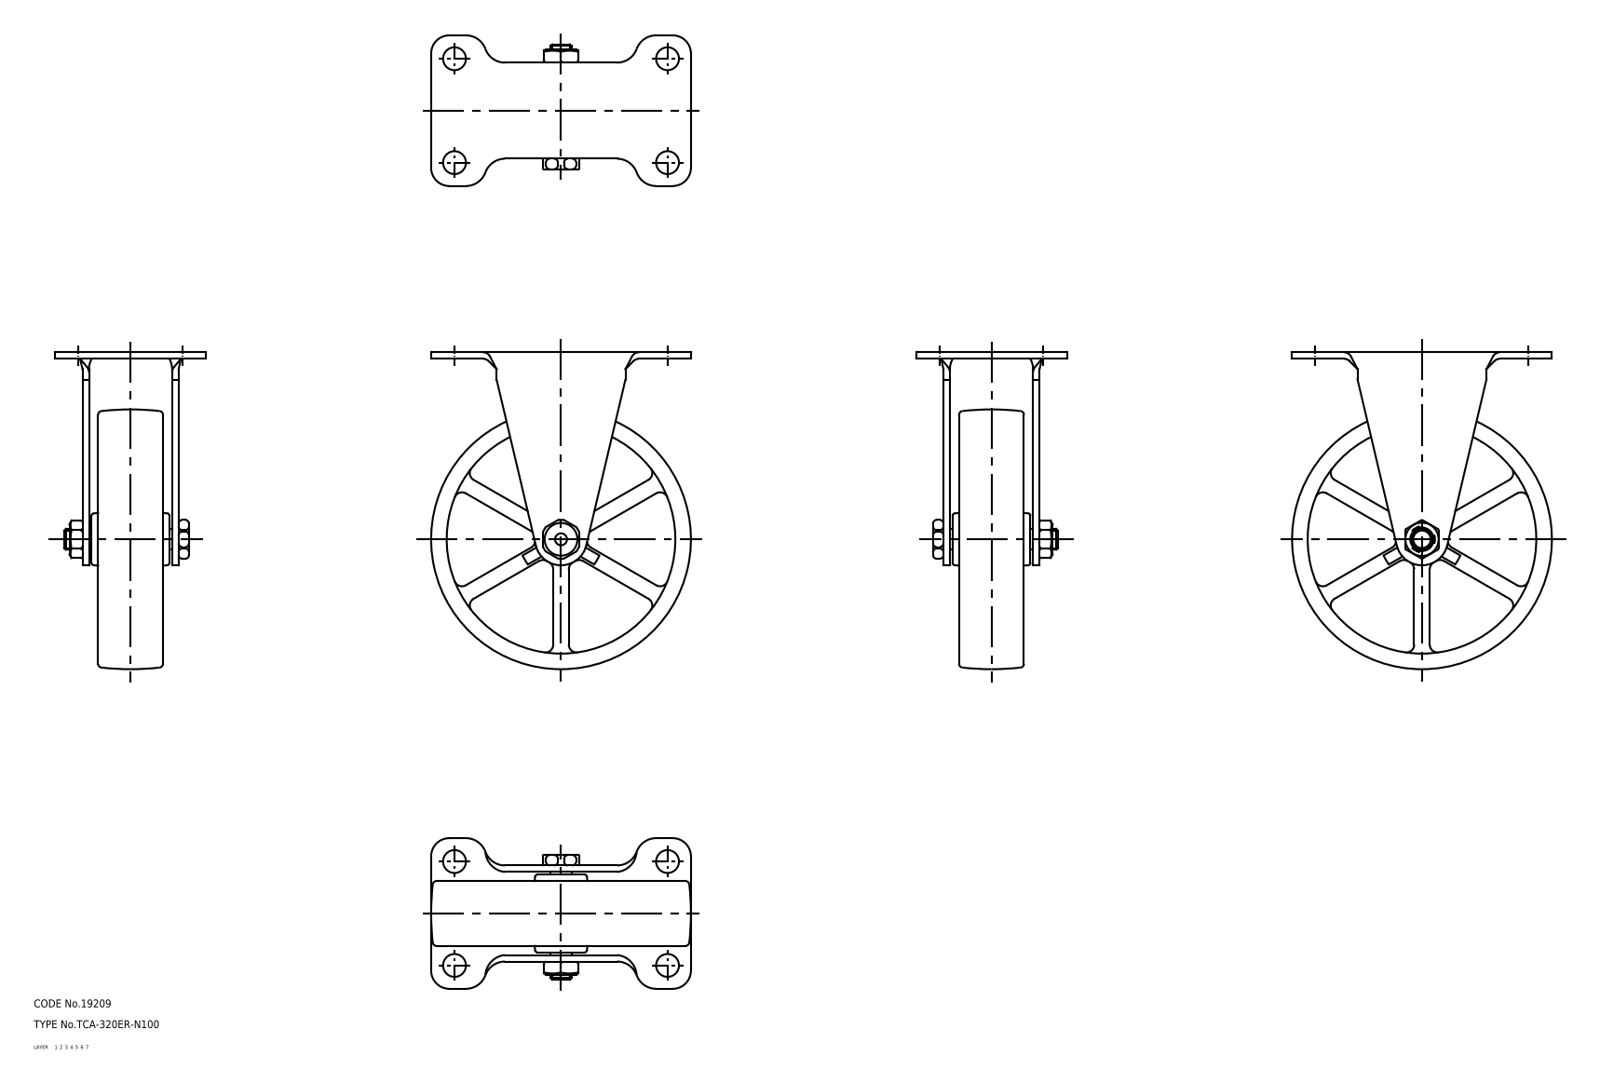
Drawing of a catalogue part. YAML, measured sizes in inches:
part_name: "wheel; axle; 320ER_N100_2741_36"
step_written_by: "CADfix (AUTOMOTIVE_DESIGN)"
units: inches
bodies: {solids: 3, faces: 549, planar: 0, cylindrical: 0, other: 549}
overall_size: [4.803, 3.937, 2.283]
volume: 10.39
surface_area: 78.22
